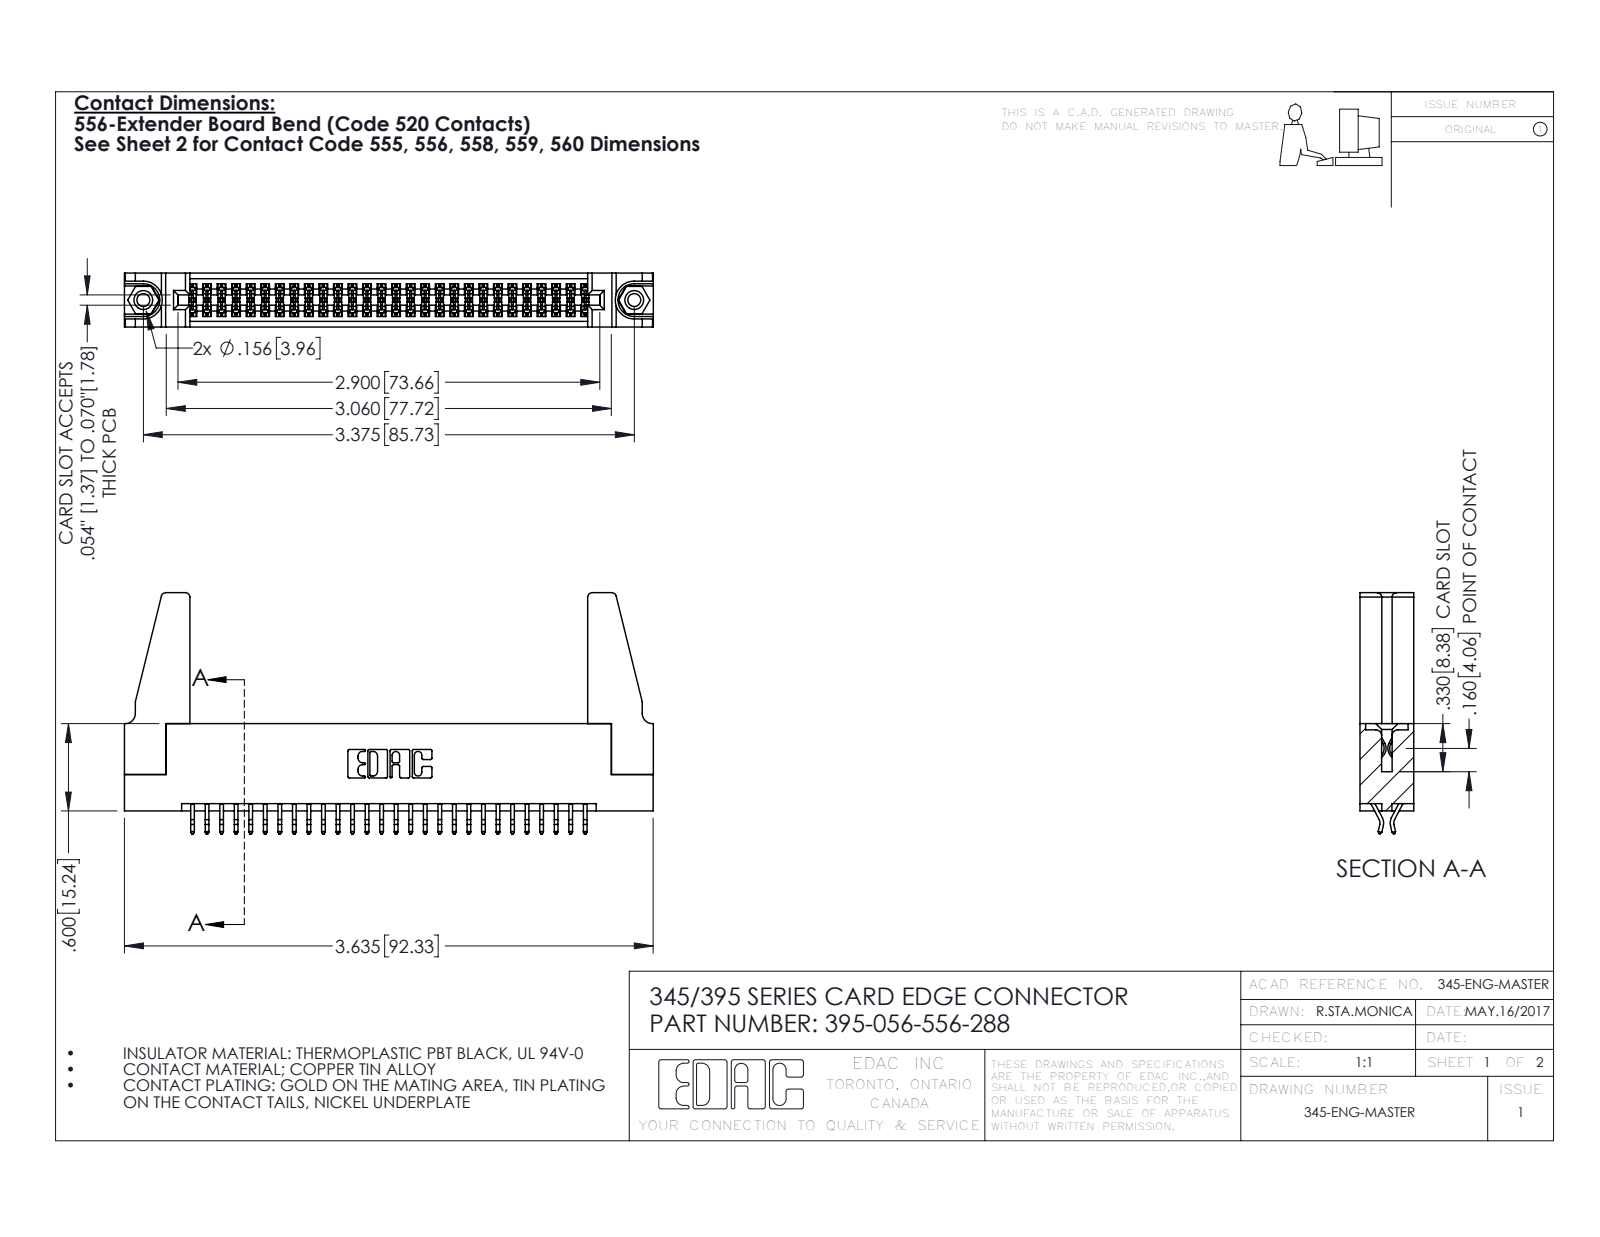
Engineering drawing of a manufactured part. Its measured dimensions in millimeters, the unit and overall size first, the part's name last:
Units: millimetres
Overall size (bounding box): 92.4 × 42.1 × 9.4
Round holes (diameter × count): ⌀2.3 ×2, ⌀3.2 ×2, ⌀4 ×2, ⌀1.6 ×1
Round bosses / shafts (diameter × count): ⌀3.9 ×2
Partial cylindrical surfaces — rounded edges, fillets, slot ends (radius × count): R0.2 ×84, R0.3 ×22, R0.8 ×8, R0.2 ×6, R0.8 ×6, R0.7 ×3, R0.3 ×2, R0.4 ×2
Main face-to-face distances: 1.8, 7.6, 9.4, 5.1, 0.6, 2.5, 6.9, 5.7, 4.4, 3.8
Hole centre spacings: 6.9, 79.8, 85.7
Volume: 12 100 mm³ · Surface area: 15 870 mm²
Bodies: 61 solids, 3386 faces (2224 planar, 1146 cylindrical, 16 other)
Part name (STEP PRODUCT): 395-056-556-288; 345 Part_Flush Mounting Lugs - 0.156 Dia-TH; 345-292-001_556 Tail; 345-250-001_345-250-001-102 (+1 more)
STEP written by: SolidWorks 2016 (CONFIG_CONTROL_DESIGN)
